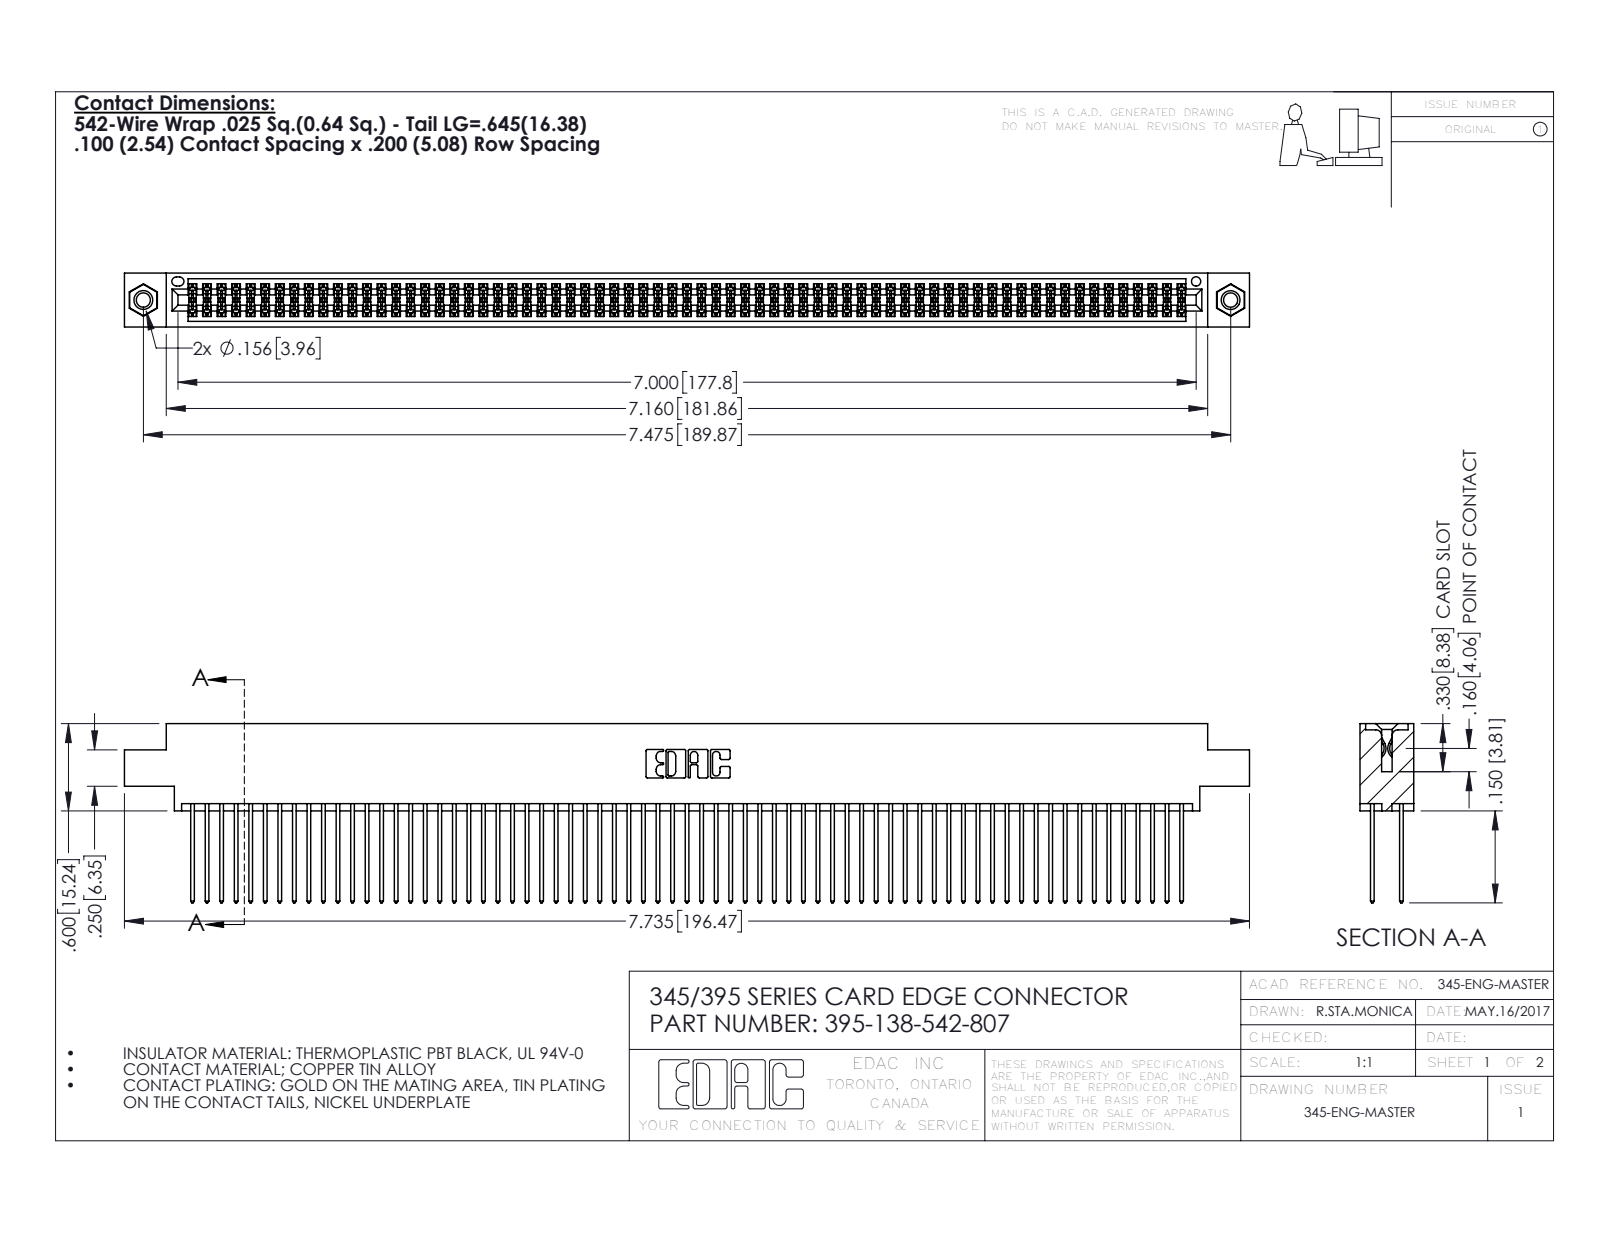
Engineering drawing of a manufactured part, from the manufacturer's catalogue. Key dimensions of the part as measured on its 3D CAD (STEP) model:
Part name (STEP PRODUCT): 345-292-001_345-293-142; 395-138-542-807; 345 Part_0.170 Offset - 0.156 Dia-TI; 345-250-001_345-250-005-103
STEP written by: SolidWorks 2016 (CONFIG_CONTROL_DESIGN)
Units: inches
Bodies: 141 solids, 7090 faces (4670 planar, 2404 cylindrical, 16 other)
Overall size (bounding box): 7.735 × 1.232 × 0.37
Volume: 1.211 in³ · Surface area: 51.22 in²
Round holes (diameter × count): ⌀0.098 ×2, ⌀0.125 ×2, ⌀0.156 ×2, ⌀0.064 ×1
Round bosses / shafts (diameter × count): ⌀0.155 ×2
Partial cylindrical surfaces — rounded edges, fillets, slot ends (radius × count): R0.006 ×207, R0.01 ×138, R0.01 ×22, R0.007 ×6, R0.031 ×6, R0.026 ×3, R0.014 ×2, R0.019 ×2
Main face-to-face distances: 0.072, 0.298, 0.2, 0.098, 0.272, 0.025, 0.225, 0.37, 0.175, 0.149
Hole centre spacings: 0.27, 7.239, 7.475
